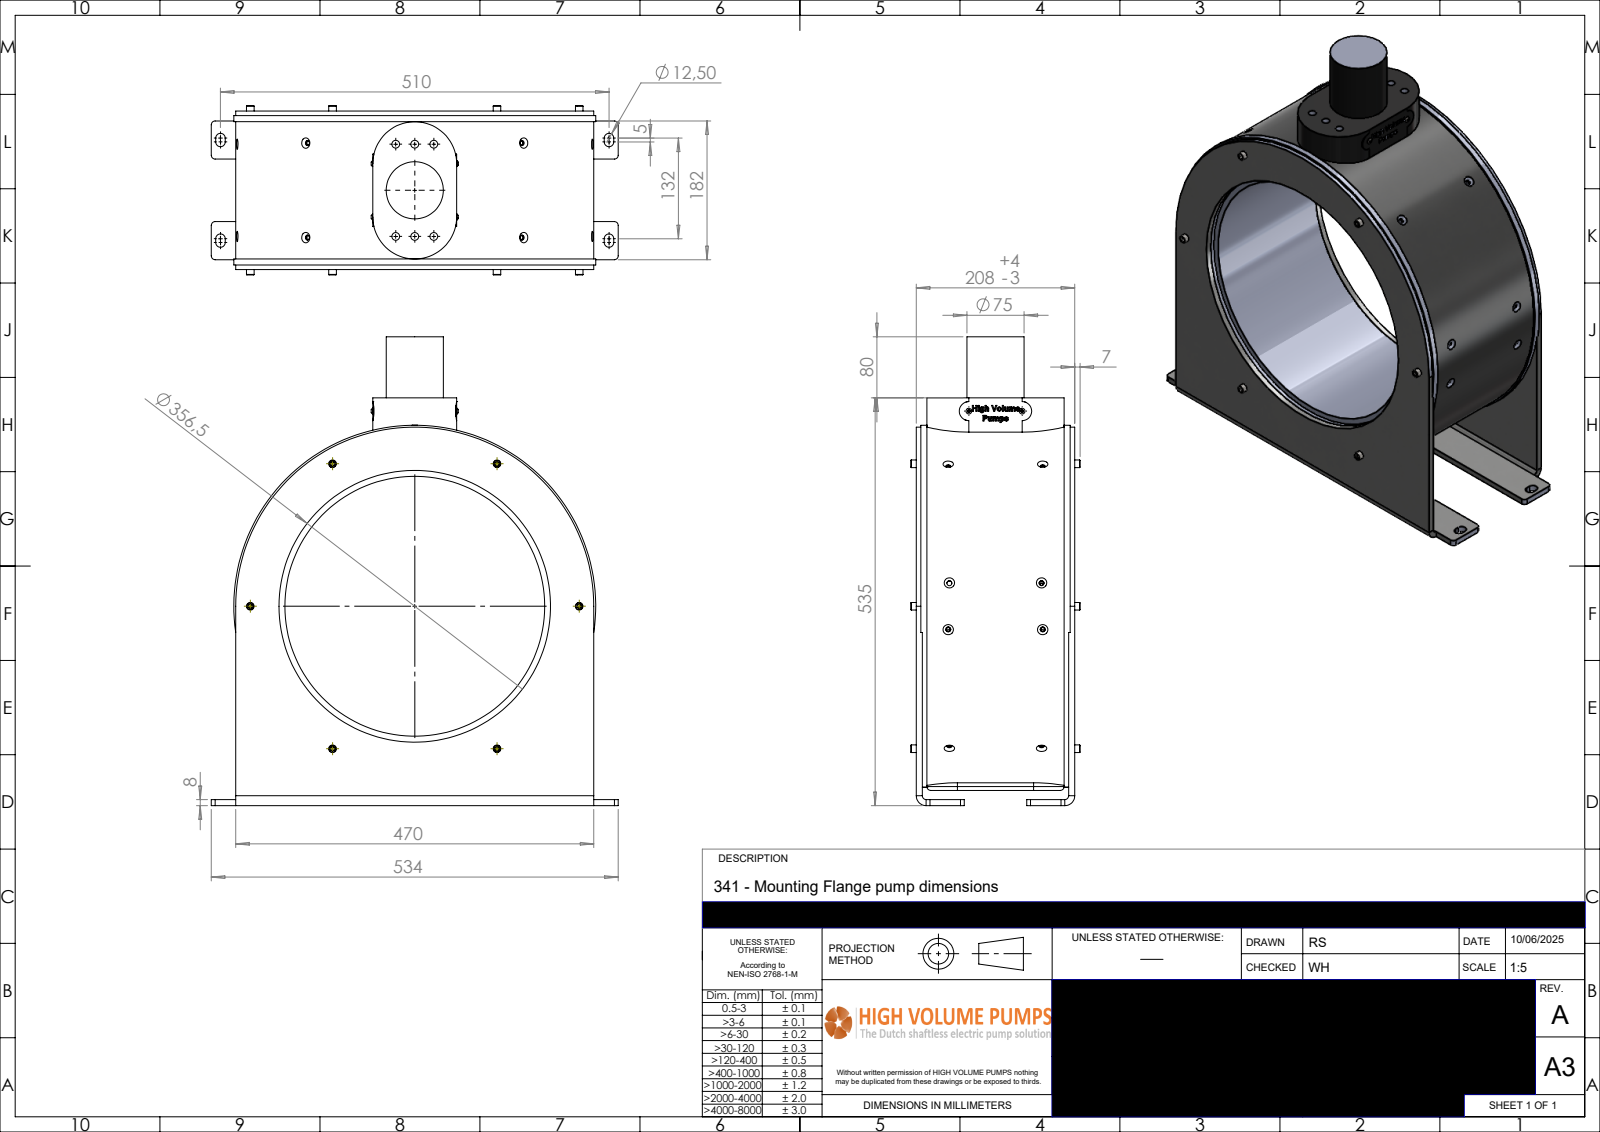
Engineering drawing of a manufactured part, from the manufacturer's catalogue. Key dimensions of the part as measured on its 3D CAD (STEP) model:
Part name (STEP PRODUCT): P-341-030-rev-A-MF
STEP written by: SolidWorks 2024 (AUTOMOTIVE_DESIGN)
Units: millimetres
Bodies: 1 solid, 1004 faces (597 planar, 111 cylindrical, 296 other)
Overall size (bounding box): 615.07 × 534 × 222
Volume: 19 040 000 mm³ · Surface area: 1 023 000 mm²
Round holes (diameter × count): ⌀6.6 ×16, ⌀5 ×14, ⌀10.2 ×6, ⌀341 ×1, ⌀356.5 ×1, ⌀357 ×1
Round bosses / shafts (diameter × count): ⌀11.57 ×6, ⌀10 ×6, ⌀7.6 ×2, ⌀475 ×1, ⌀470 ×1, ⌀75 ×1
Partial cylindrical surfaces — rounded edges, fillets, slot ends (radius × count): R5 ×15, R6.25 ×8, R12.5 ×2, R13 ×2, R40 ×2, R55 ×2
Main face-to-face distances: 8, 208, 200, 6, 194, 192, 14, 186, 180, 535.07
Hole centre spacings: 122.5, 121, 1.52, 1.56, 25, 123.56, 124, 50
